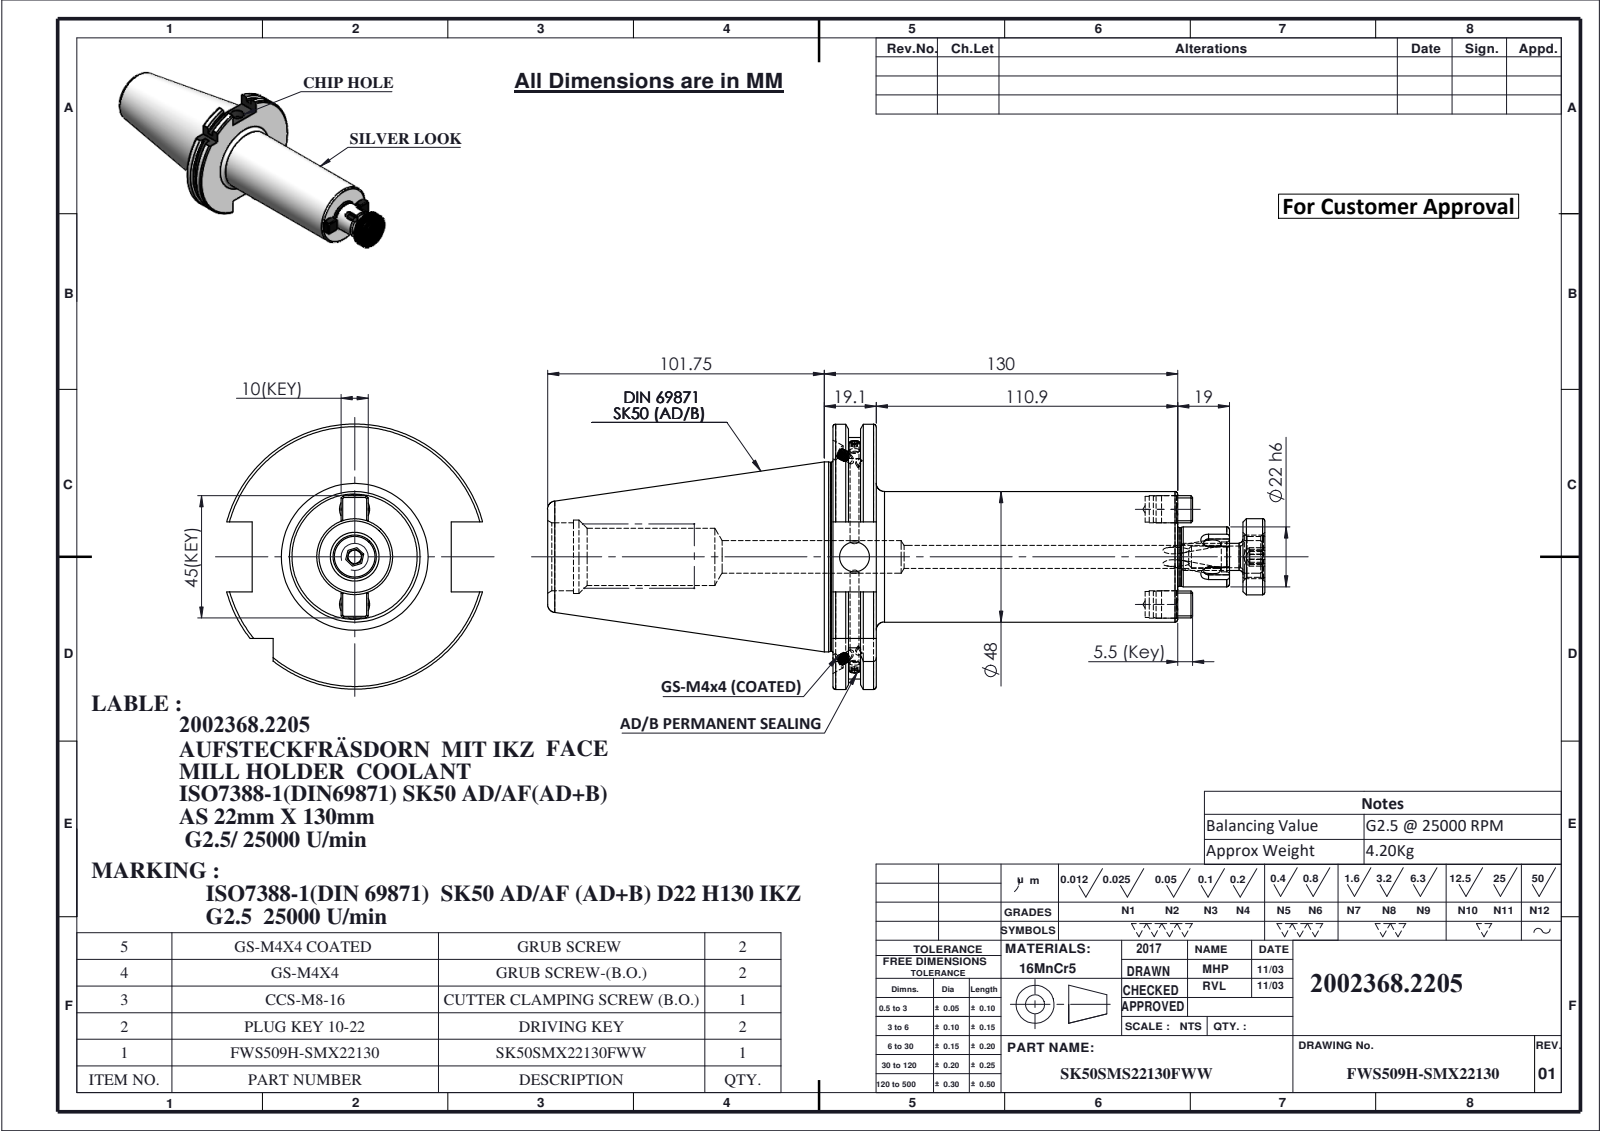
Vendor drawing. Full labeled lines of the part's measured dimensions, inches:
Part name (STEP PRODUCT): CCS-M10-22 LONG; CCS-M10-22-1; SK50SMX22130FWW; CCS-M8-16-1 (+6 more)
STEP written by: SolidWorks 2024 (CONFIG_CONTROL_DESIGN)
Units: inches
Bodies: 10 solids, 472 faces (146 planar, 133 cylindrical, 193 other)
Overall size (bounding box): 10.384 × 3.839 × 3.703
Volume: 32.93 in³ · Surface area: 112 in²
Round holes (diameter × count): ⌀0.118 ×4, ⌀0.236 ×3, ⌀0.126 ×2, ⌀0.374 ×2, ⌀0.394 ×2, ⌀0.433 ×2, ⌀0.13 ×1, ⌀0.335 ×1, ⌀0.472 ×1, ⌀0.591 ×1, ⌀0.827 ×1, ⌀0.984 ×1
Round bosses / shafts (diameter × count): ⌀0.157 ×4, ⌀0.394 ×2, ⌀0.393 ×2, ⌀0.114 ×2, ⌀2.75 ×1, ⌀2.734 ×1, ⌀1.89 ×1, ⌀1.102 ×1
Partial cylindrical surfaces — rounded edges, fillets, slot ends (radius × count): R0.079 ×4, R0.256 ×2, R1.768 ×1, R1.919 ×1
Main face-to-face distances: 0.626, 4.992, 4.366, 0.223, 0.403, 4.769, 0.399, 0.176, 0.227, 4.593
Hole centre spacings: 0.689, 1.378
